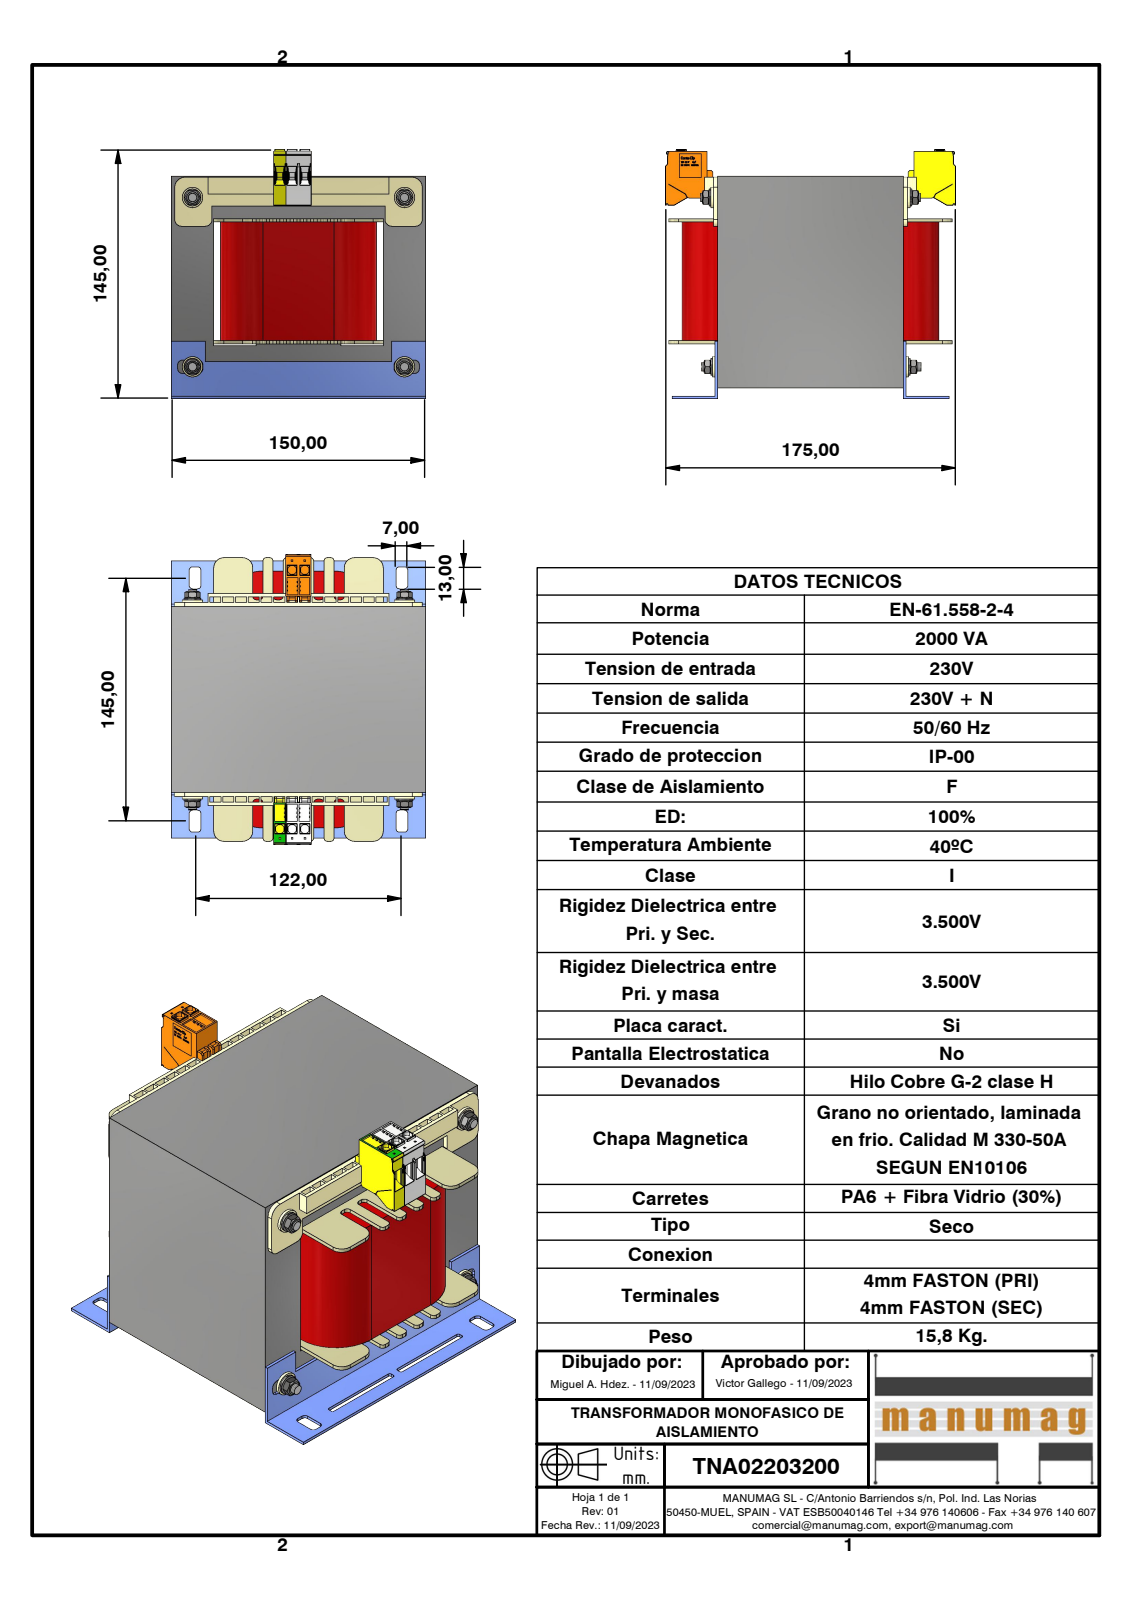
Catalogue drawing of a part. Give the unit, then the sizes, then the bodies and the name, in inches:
Units: inches
Overall size (bounding box): 6.768 × 5.906 × 5.803
Round holes (diameter × count): ⌀0.163 ×4, ⌀0.197 ×4, ⌀0.209 ×4, ⌀0.315 ×4
Round bosses / shafts (diameter × count): ⌀0.472 ×4, ⌀0.394 ×4, ⌀0.232 ×4
Partial cylindrical surfaces — rounded edges, fillets, slot ends (radius × count): R0.006 ×216, R0.008 ×70, R0.079 ×52, R0.039 ×24, R0.02 ×18, R0.012 ×12, R0.236 ×10, R0.118 ×8
Main face-to-face distances: 3.937, 0.984, 1.969, 4.921, 4.331, 2.953, 0.059, 5.906, 0.827, 0.039
Hole centre spacings: 3.937, 4.921, 6.302
Volume: 140.2 in³ · Surface area: 484.4 in²
Bodies: 37 solids, 5349 faces (4383 planar, 678 cylindrical, 288 other)
Part name (STEP PRODUCT): TNA02203200; EI150 x 125 - 110 (RC50); AF50DIN; EI150 (+8 more)
STEP written by: Autodesk Inventor 2023 (AUTOMOTIVE_DESIGN)
